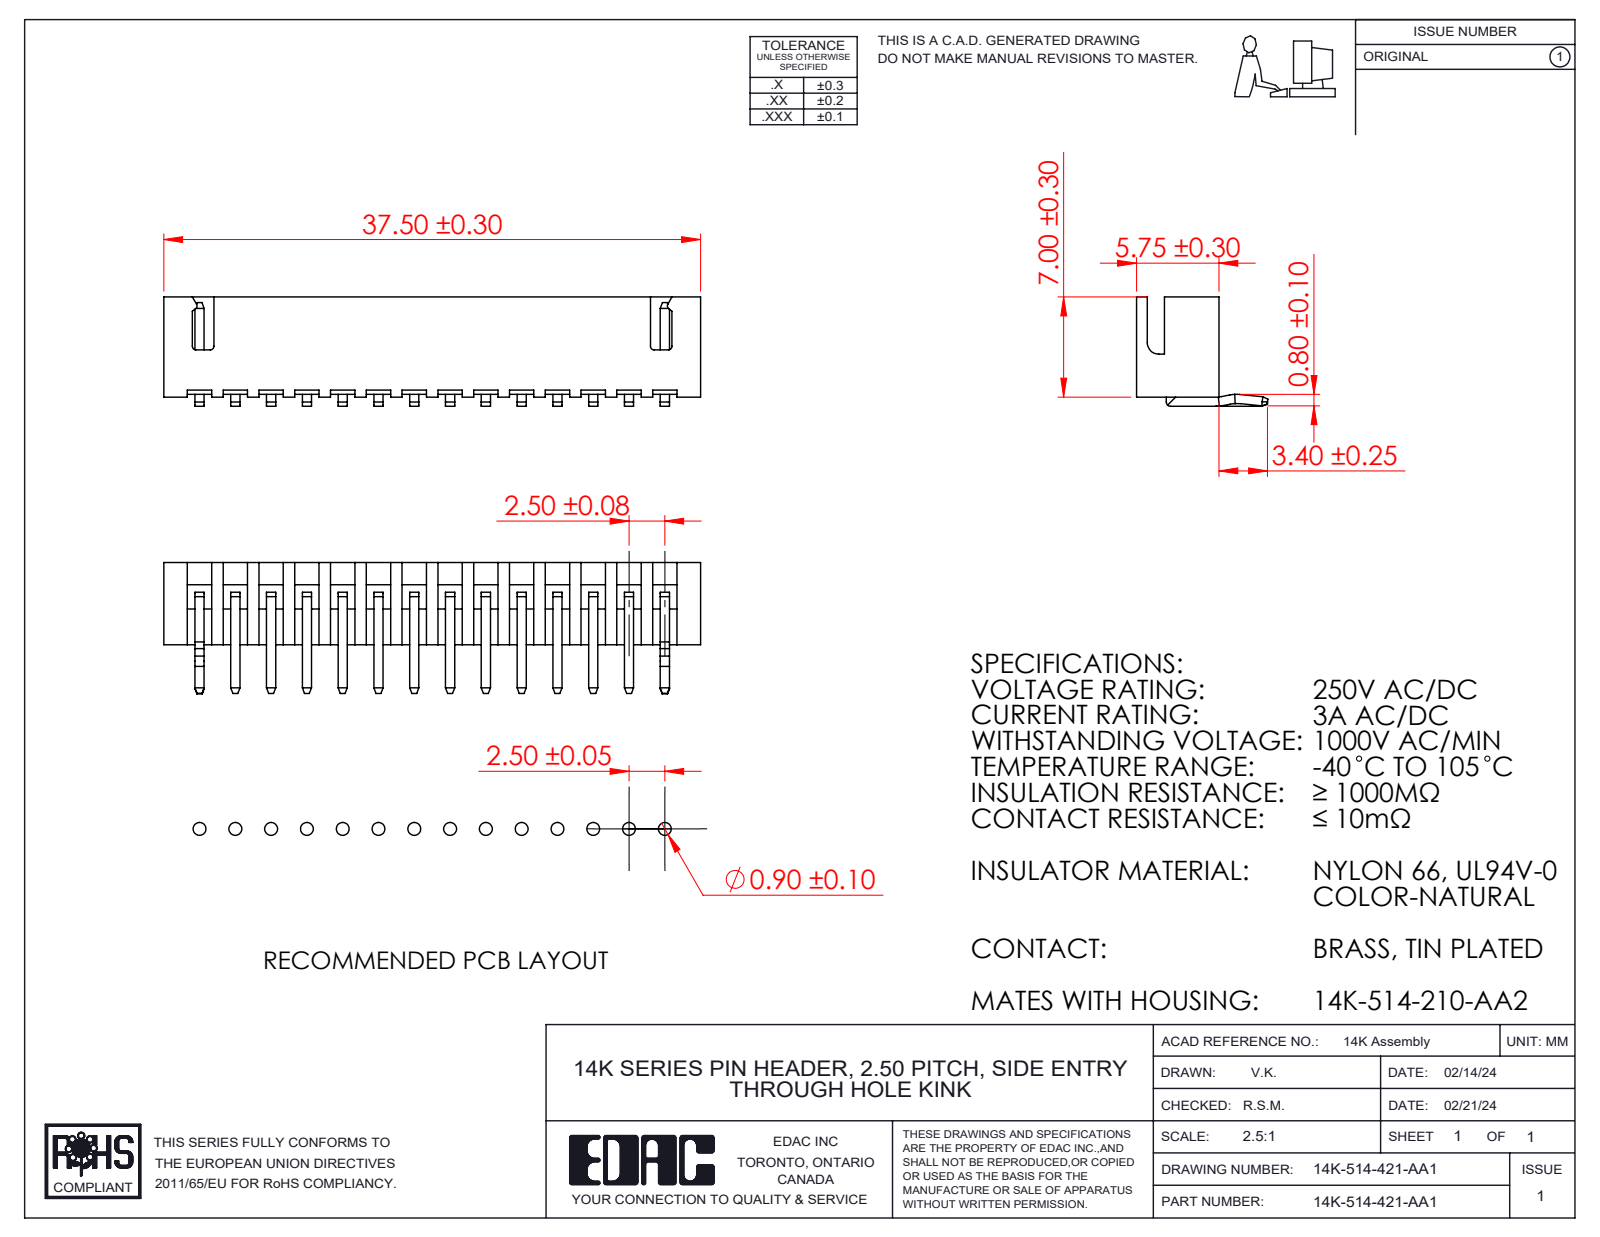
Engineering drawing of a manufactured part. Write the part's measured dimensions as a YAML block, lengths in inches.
part_name: "14K Series Pin_16; 14K Series Pin_21; 14K-514-421-AA1; 14K Series Pin Header Insulator_514"
step_written_by: "SolidWorks 2023 (CONFIG_CONTROL_DESIGN)"
units: inches
bodies: {solids: 15, faces: 516, planar: 467, cylindrical: 49, other: 0}
overall_size: [1.476, 0.361, 0.301]
volume: 0.044
surface_area: 3.12
partial_cylinders:
  - {radius: 0.01, count: 6}
  - {radius: 0.098, count: 4}
  - {radius: 0.012, count: 2}
  - {radius: 0.031, count: 1}
face_to_face_distances: [0.197, 0.03, 0.227, 0.167, 0.025, 0.098, 0.295, 0.394, 0.492, 0.591]
